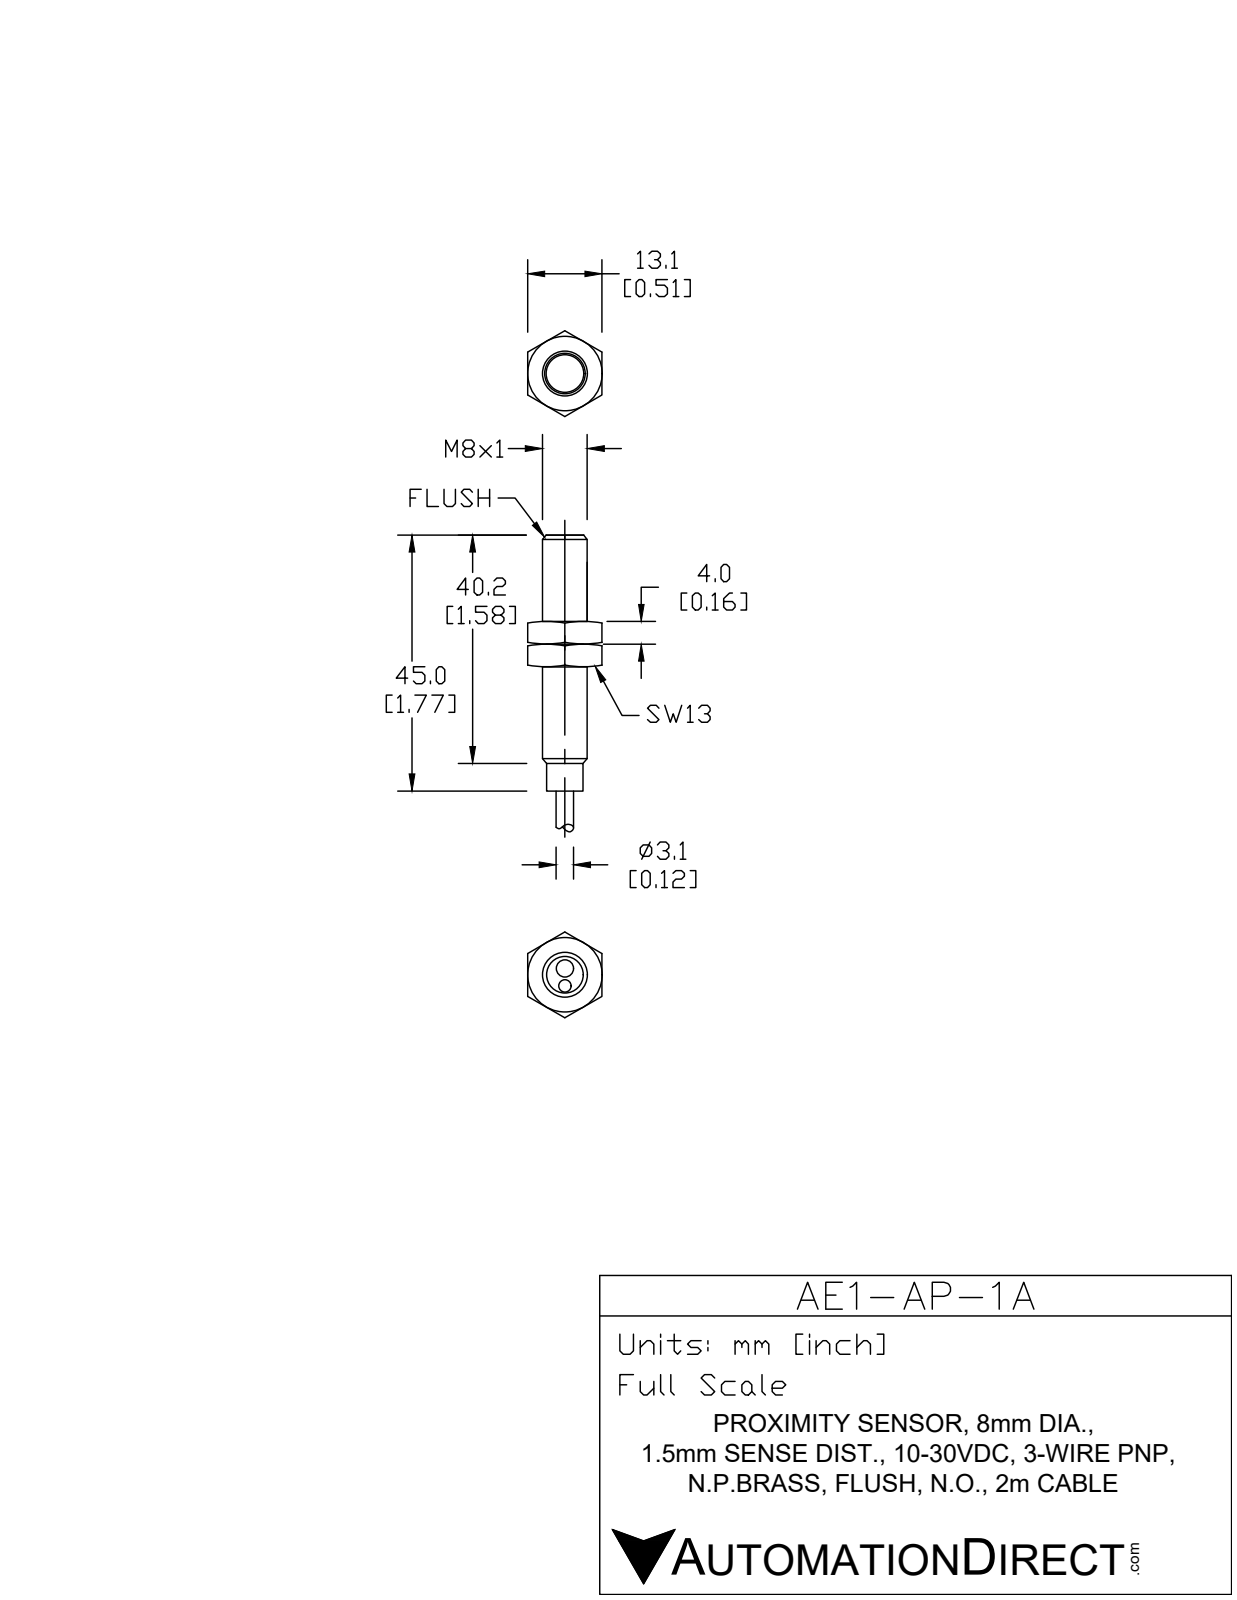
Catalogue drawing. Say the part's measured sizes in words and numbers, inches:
The part is named "AE1-AP-1A". Its 3-D file was written by "SolidWorks 2017 (AUTOMOTIVE_DESIGN)". It is 4 solids with 30 faces: 10 planar, 12 cylindrical and 8 other. Overall it measures 3.252 by 0.315 by 0.315 inches. Its volume is 0.148 cubic inches and its surface area 2.704 square inches. Round holes: 1 of diameter 0.122, 1 of diameter 0.228. Round bosses or shafts: 1 of diameter 0.315, 1 of diameter 0.256, 1 of diameter 0.254. The main face-to-face distances are 1.571, 1.583, 1.752, 1.74, 0.169, 0.094, 1.677, 1.665, 0.075, 3.252. The hole center spacings are 0.045.
